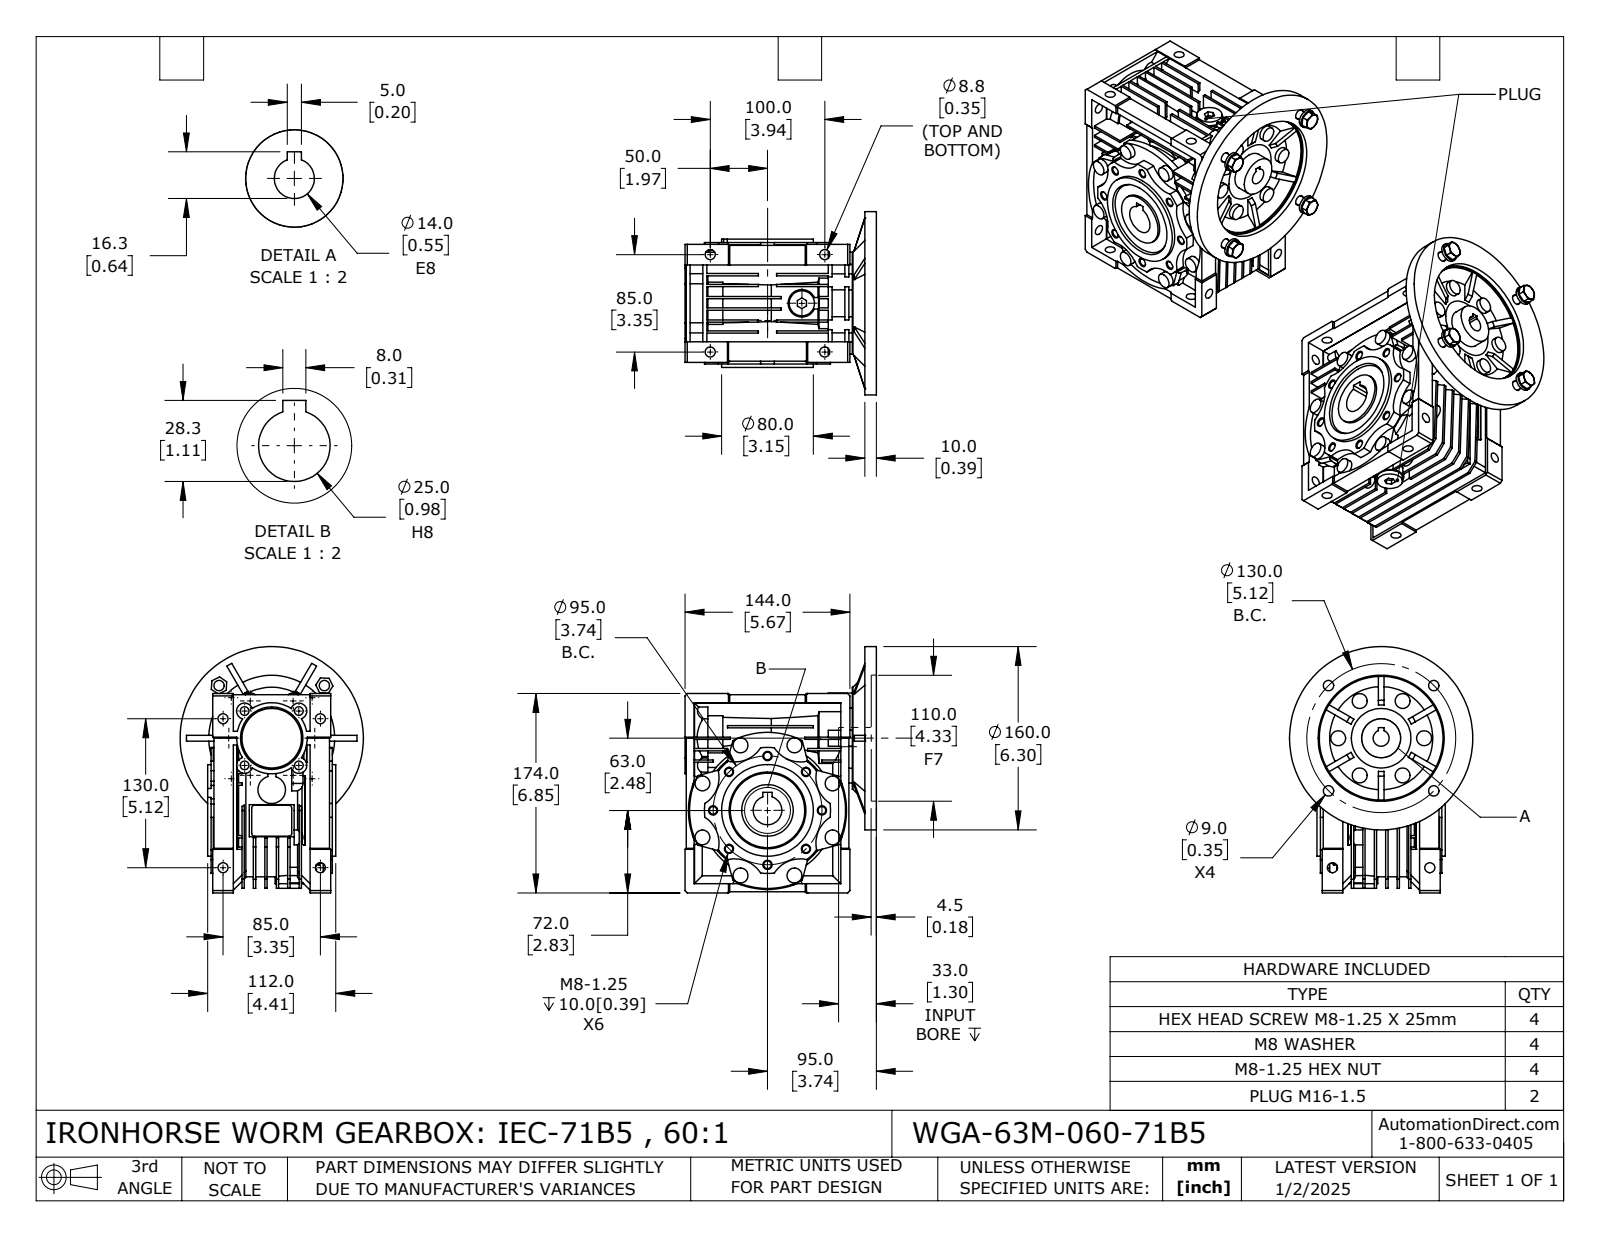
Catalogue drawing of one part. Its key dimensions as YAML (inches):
part_name: "WGA-63M-060-71B5"
step_written_by: "SolidWorks 2024 (CONFIG_CONTROL_DESIGN)"
units: inches
bodies: {solids: 20, faces: 1516, planar: 887, cylindrical: 379, other: 250}
overall_size: [8.465, 7.204, 6.299]
volume: 117.1
surface_area: 575.6
round_holes:
  - {diameter: 0.262, count: 8}
  - {diameter: 0.346, count: 8}
  - {diameter: 0.268, count: 4}
  - {diameter: 0.298, count: 4}
  - {diameter: 0.315, count: 4}
  - {diameter: 0.354, count: 4}
  - {diameter: 0.359, count: 4}
  - {diameter: 0.571, count: 2}
  - {diameter: 0.551, count: 1}
  - {diameter: 0.591, count: 1}
  - {diameter: 0.984, count: 1}
  - {diameter: 1.339, count: 1}
round_bosses_or_shafts:
  - {diameter: 0.512, count: 14}
  - {diameter: 0.63, count: 4}
  - {diameter: 0.945, count: 3}
  - {diameter: 0.866, count: 2}
  - {diameter: 0.622, count: 2}
  - {diameter: 0.539, count: 2}
  - {diameter: 6.299, count: 1}
  - {diameter: 4.331, count: 1}
partial_cylinders:
  - {radius: 0.276, count: 10}
  - {radius: 1.063, count: 8}
  - {radius: 0.098, count: 4}
  - {radius: 0.329, count: 1}
  - {radius: 1.161, count: 1}
  - {radius: 1.201, count: 1}
  - {radius: 1.654, count: 1}
  - {radius: 2.283, count: 1}
face_to_face_distances: [0.394, 0.315, 0.787, 0.079, 1.181, 0.472, 0.276, 0.709, 1.575, 0.039]
hole_center_spacings: [1.431, 1.87, 2.645, 2.879, 3.456, 1.24, 1.319, 1.865]
